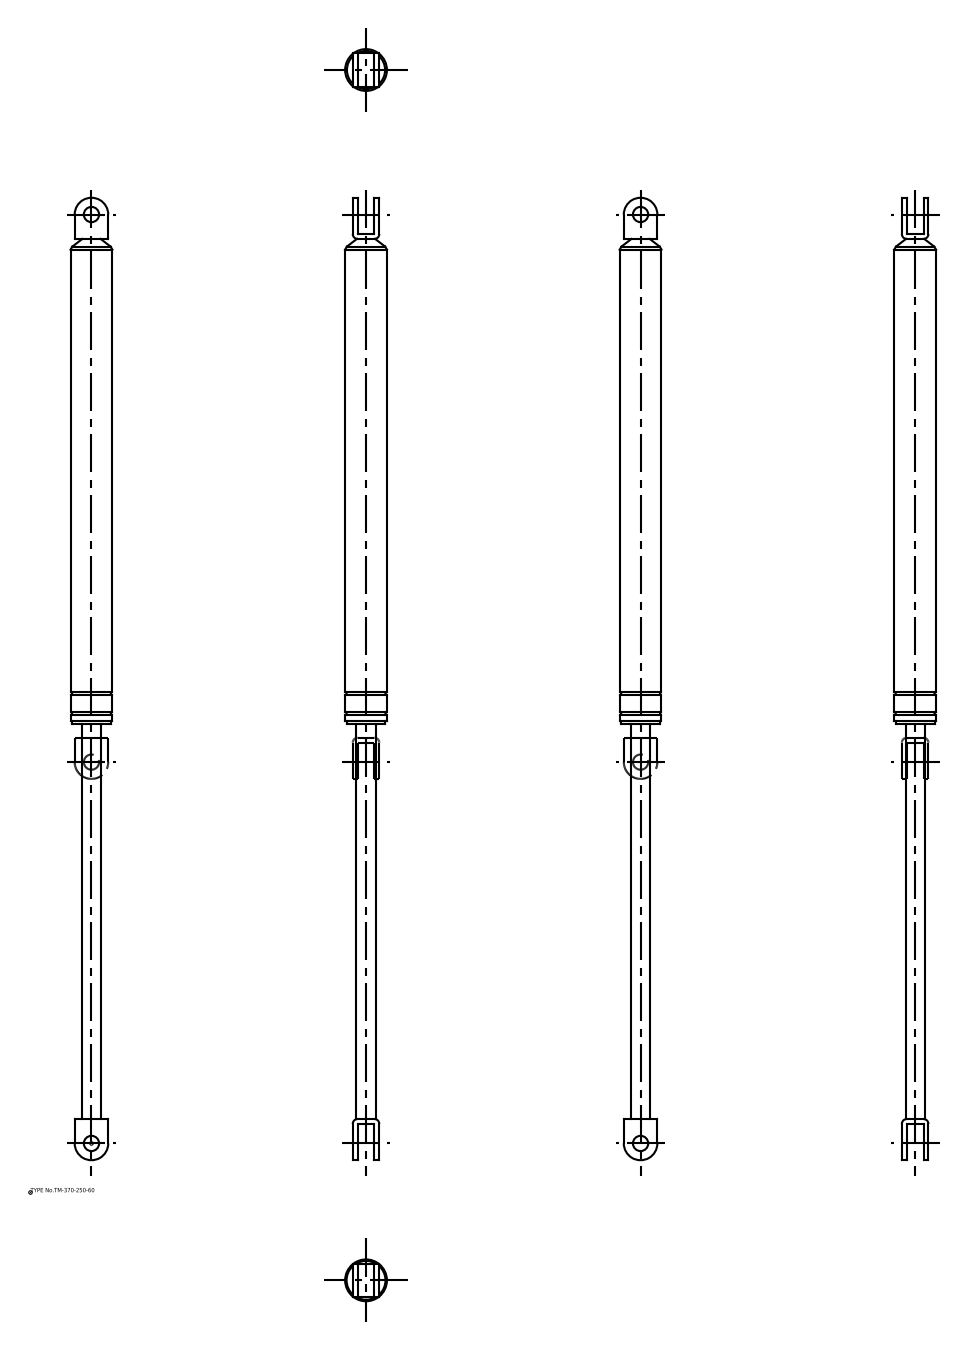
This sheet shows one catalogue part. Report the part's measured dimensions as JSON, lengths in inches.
{"part_name": "TM_370_250_60; TM_370_250_60_div", "step_written_by": "spGate 16.7.1 (AUTOMOTIVE_DESIGN)", "units": "inches", "bodies": {"solids": 2, "faces": 64, "planar": 22, "cylindrical": 32, "other": 10}, "overall_size": [24.843, 1.11, 1.11], "volume_in3": 13.73, "surface_area_in2": 68.7, "round_holes": [[0.394, 2]], "round_bosses_or_shafts": [[1.11, 1], [1.079, 1], [1.004, 1], [0.492, 1]], "partial_cylinders_radius": [[0.126, 4], [0.433, 2]], "face_to_face_distances": [0.126, 0.559, 0.685, 0.433, 0.866, 22.843, 10.323, 22.969, 12.646, 12.52], "hole_center_spacings": [23.976]}
